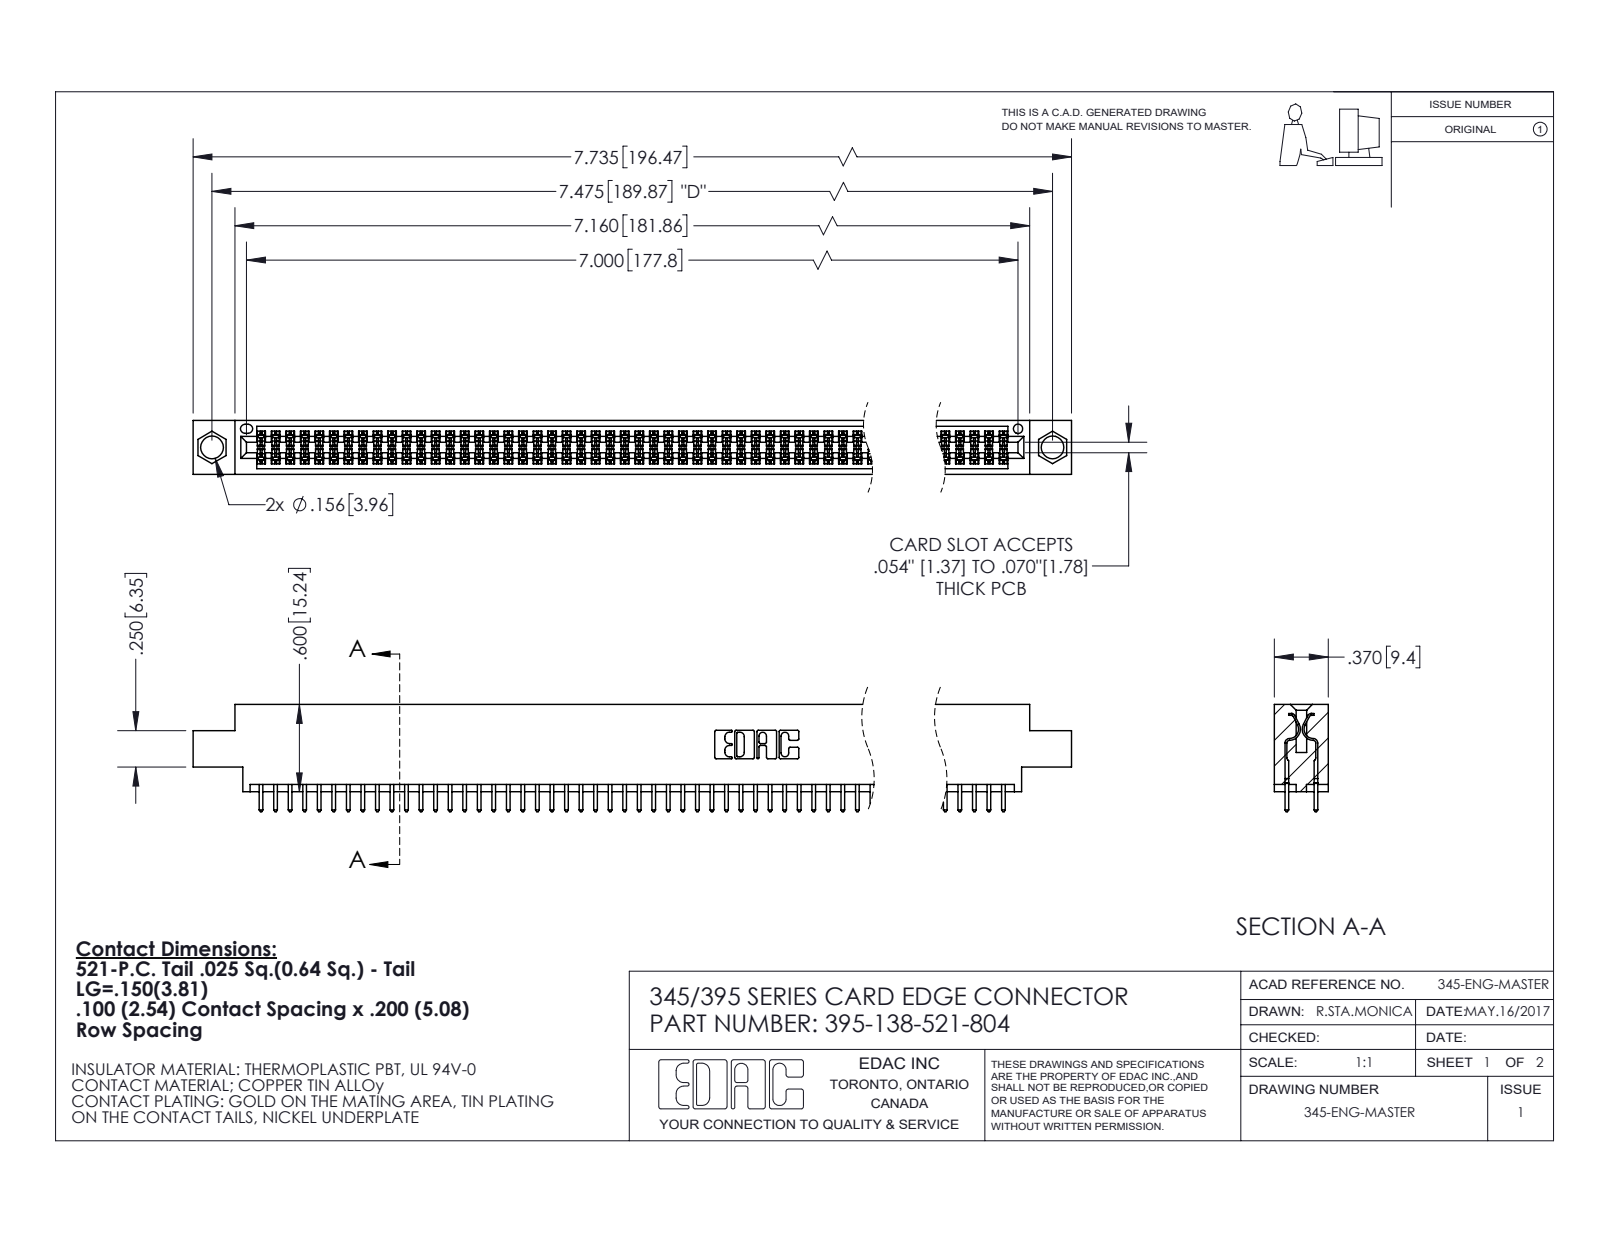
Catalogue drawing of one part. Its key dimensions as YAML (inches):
part_name: "395-138-521-804; 345-292-001_345-293-121; 345 Part_0.170 Offset - 0.156 Dia-TI"
step_written_by: "SolidWorks 2020 (CONFIG_CONTROL_DESIGN)"
units: inches
bodies: {solids: 139, faces: 7044, planar: 4652, cylindrical: 2392, other: 0}
overall_size: [7.735, 0.737, 0.37]
volume: 1.163
surface_area: 43.9
round_holes:
  - {diameter: 0.156, count: 2}
  - {diameter: 0.064, count: 1}
partial_cylinders:
  - {radius: 0.006, count: 208}
  - {radius: 0.01, count: 138}
  - {radius: 0.01, count: 22}
  - {radius: 0.007, count: 6}
  - {radius: 0.031, count: 6}
  - {radius: 0.026, count: 3}
  - {radius: 0.014, count: 2}
  - {radius: 0.019, count: 2}
face_to_face_distances: [0.072, 0.298, 0.2, 0.37, 0.098, 0.272, 0.025, 0.225, 0.175, 0.149]
hole_center_spacings: [0.27, 7.239, 7.475]
